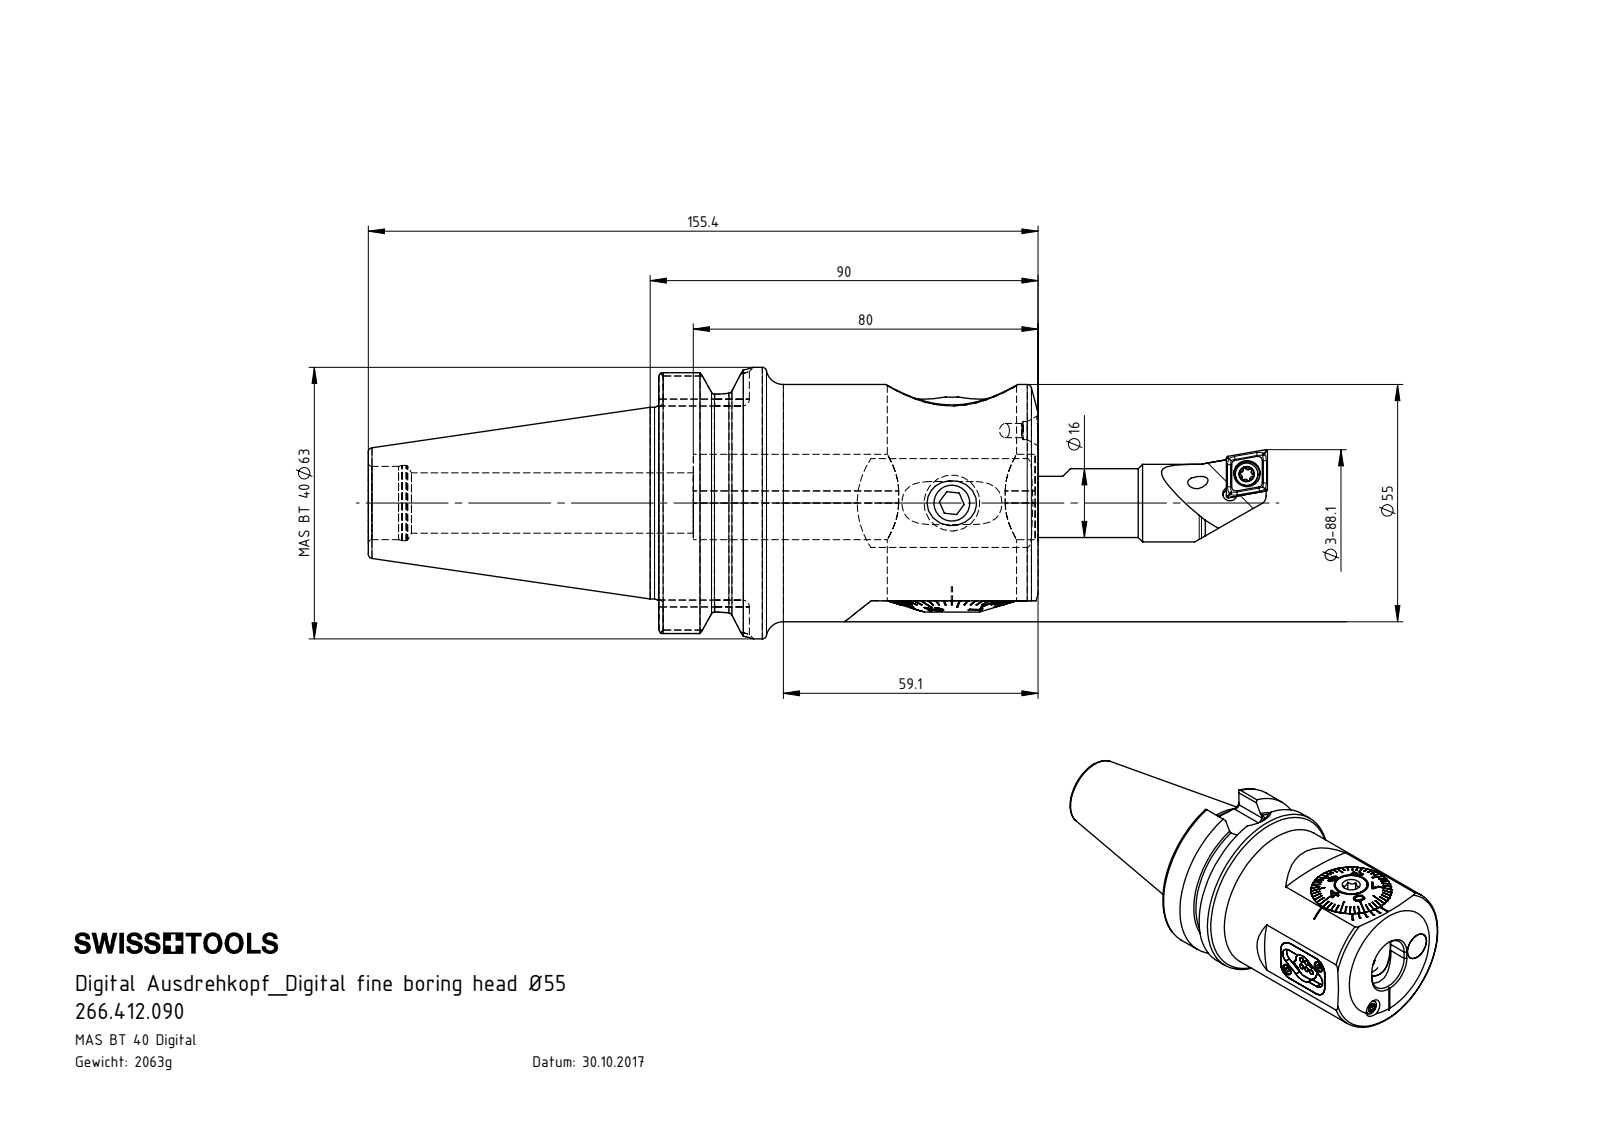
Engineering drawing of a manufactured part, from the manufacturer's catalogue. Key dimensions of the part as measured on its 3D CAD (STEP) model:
Part name (STEP PRODUCT): A55-BG3.011.033_A_gekrzt; CCMT09T304; 266.412.090; A55-BG1.DA2.041_bewegliche Schrauben (+8 more)
STEP written by: SolidWorks 2017 (CONFIG_CONTROL_DESIGN)
Units: millimetres
Bodies: 27 solids, 1179 faces (485 planar, 309 cylindrical, 385 other)
Overall size (bounding box): 208.65 × 63 × 63
Volume: 263 812 mm³ · Surface area: 67 334 mm²
Round holes (diameter × count): ⌀3.2 ×4, ⌀1.6 ×3, ⌀3.3 ×3, ⌀4.2 ×3, ⌀8.5 ×3, ⌀2.2 ×2, ⌀3 ×2, ⌀14 ×2, ⌀4.4 ×1, ⌀6.1 ×1, ⌀8 ×1, ⌀10 ×1
Round bosses / shafts (diameter × count): ⌀1.9 ×6, ⌀10 ×3, ⌀18 ×2, ⌀5.25 ×2, ⌀4 ×2, ⌀3.8 ×2, ⌀2 ×2, ⌀63 ×1
Partial cylindrical surfaces — rounded edges, fillets, slot ends (radius × count): R0.34 ×12, R0.59 ×12, R1.2 ×8, R1.6 ×8, R1.1 ×6, R4.5 ×4, R3.2 ×3, R4.4 ×3
Main face-to-face distances: 88, 3.7, 2, 4, 28.85, 0.45, 2.8, 5.3, 1.2, 5.65
Hole centre spacings: 4.1, 4.32, 7.25, 8.45, 9.52, 12, 12.68, 14.5
